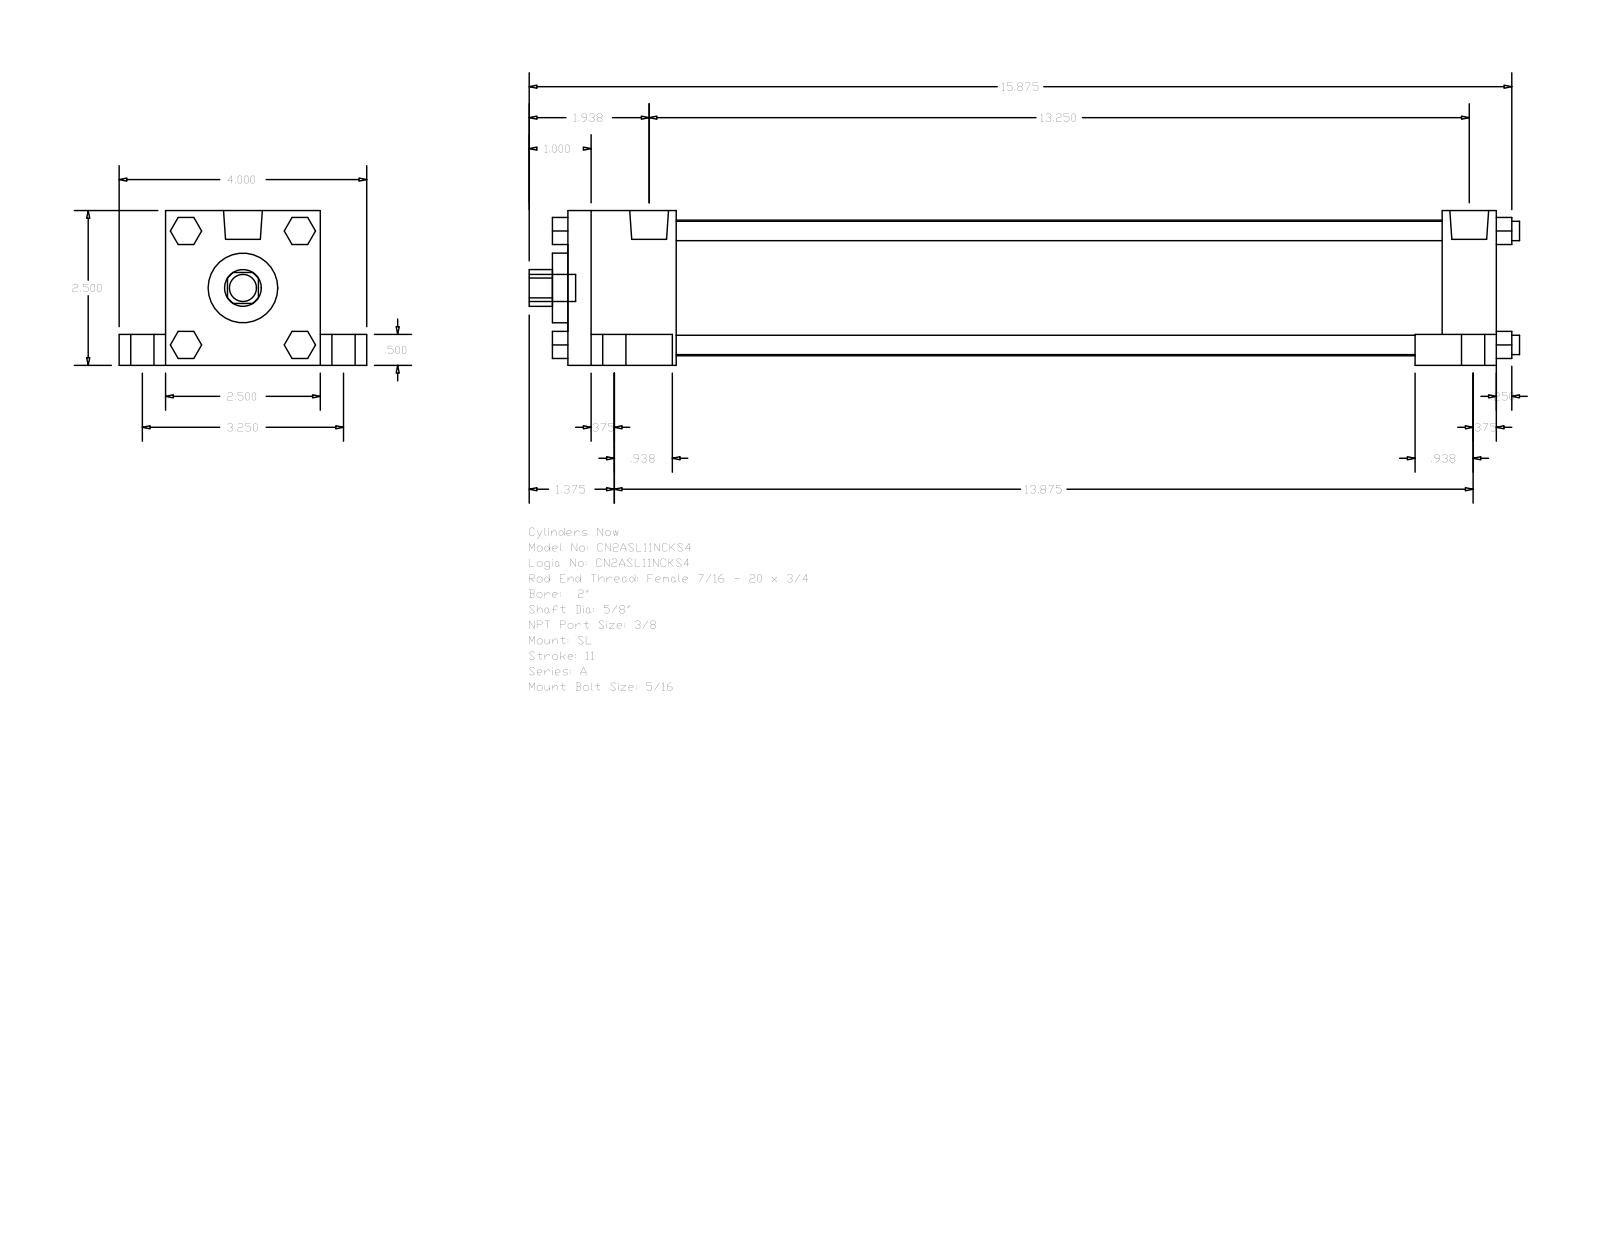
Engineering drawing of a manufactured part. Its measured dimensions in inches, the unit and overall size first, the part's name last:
Units: inches
Overall size (bounding box): 16 × 4 × 2.5
Round holes (diameter × count): ⌀0.625 ×1, ⌀1.125 ×1, ⌀2.19 ×1
Round bosses / shafts (diameter × count): ⌀0.625 ×4, ⌀0.375 ×4, ⌀0.313 ×4, ⌀0.219 ×4, ⌀0.627 ×2, ⌀0.437 ×1
Partial cylindrical surfaces — rounded edges, fillets, slot ends (radius × count): R0.297 ×1
Main face-to-face distances: 2.5, 15, 2, 0.5, 0.75, 3.25, 1.75, 13.25, 14.125, 12.375
Bodies: 0 solids, 148 faces (112 planar, 36 cylindrical, 0 other)
Part name (STEP PRODUCT): A_SL__0200_0.625
STEP written by: GSSL Pune (CONFIG_CONTROL_DESIGN)
